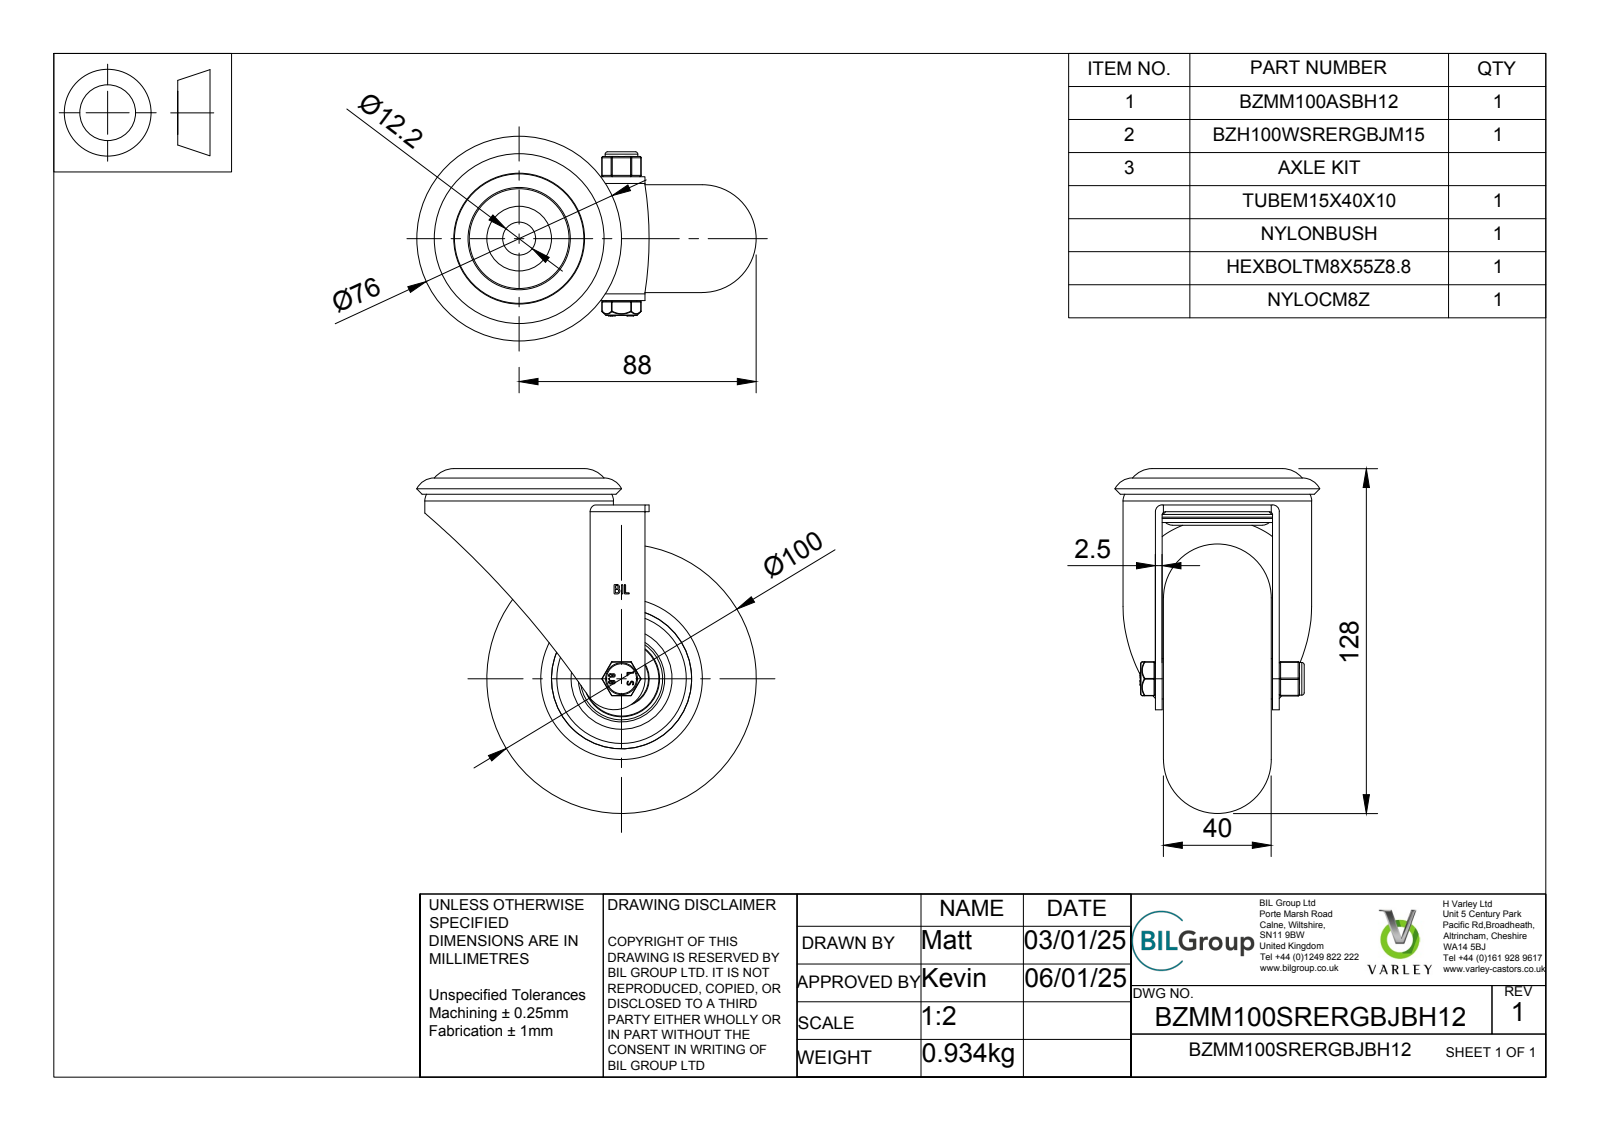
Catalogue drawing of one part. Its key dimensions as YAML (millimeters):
part_name: "BZMM100SRERGBJBH12 v3; BZMM100ASBH12 - 41 v1; ZINC PLATED PRESSED STEEL HEAD; ZINC PLATED, PRESSED STEEL FORKS (+8 more)"
step_written_by: "Autodesk Translation Framework v13.20.0.188 (AP242_MANAGED_MODEL_BASED_3D_ENGINEERING_MIM_LF)"
units: millimeters
bodies: {solids: 38, faces: 1085, planar: 360, cylindrical: 202, other: 523}
overall_size: [128, 126, 76]
volume: 304060
surface_area: 109890
round_holes:
  - {diameter: 0.66, count: 2}
  - {diameter: 8, count: 1}
  - {diameter: 8.2, count: 1}
  - {diameter: 8.6, count: 1}
  - {diameter: 10.2, count: 1}
  - {diameter: 12.2, count: 1}
  - {diameter: 15, count: 1}
  - {diameter: 20.5, count: 1}
  - {diameter: 26, count: 1}
  - {diameter: 26.8, count: 1}
  - {diameter: 28, count: 1}
  - {diameter: 28.2, count: 1}
round_bosses_or_shafts:
  - {diameter: 70, count: 1}
  - {diameter: 49.5, count: 1}
  - {diameter: 38, count: 1}
  - {diameter: 37.5, count: 1}
  - {diameter: 24, count: 1}
  - {diameter: 21.5, count: 1}
  - {diameter: 21.31, count: 1}
  - {diameter: 20, count: 1}
partial_cylinders:
  - {radius: 0.5, count: 18}
  - {radius: 0.25, count: 12}
  - {radius: 0.33, count: 4}
  - {radius: 0.64, count: 4}
  - {radius: 1.25, count: 4}
  - {radius: 0.63, count: 2}
  - {radius: 0.64, count: 2}
  - {radius: 2.5, count: 2}
face_to_face_distances: [2.5, 3, 0.5, 9, 40.5, 43, 43.5, 6.5, 34, 31]
hole_center_spacings: [3.22, 2.49]
